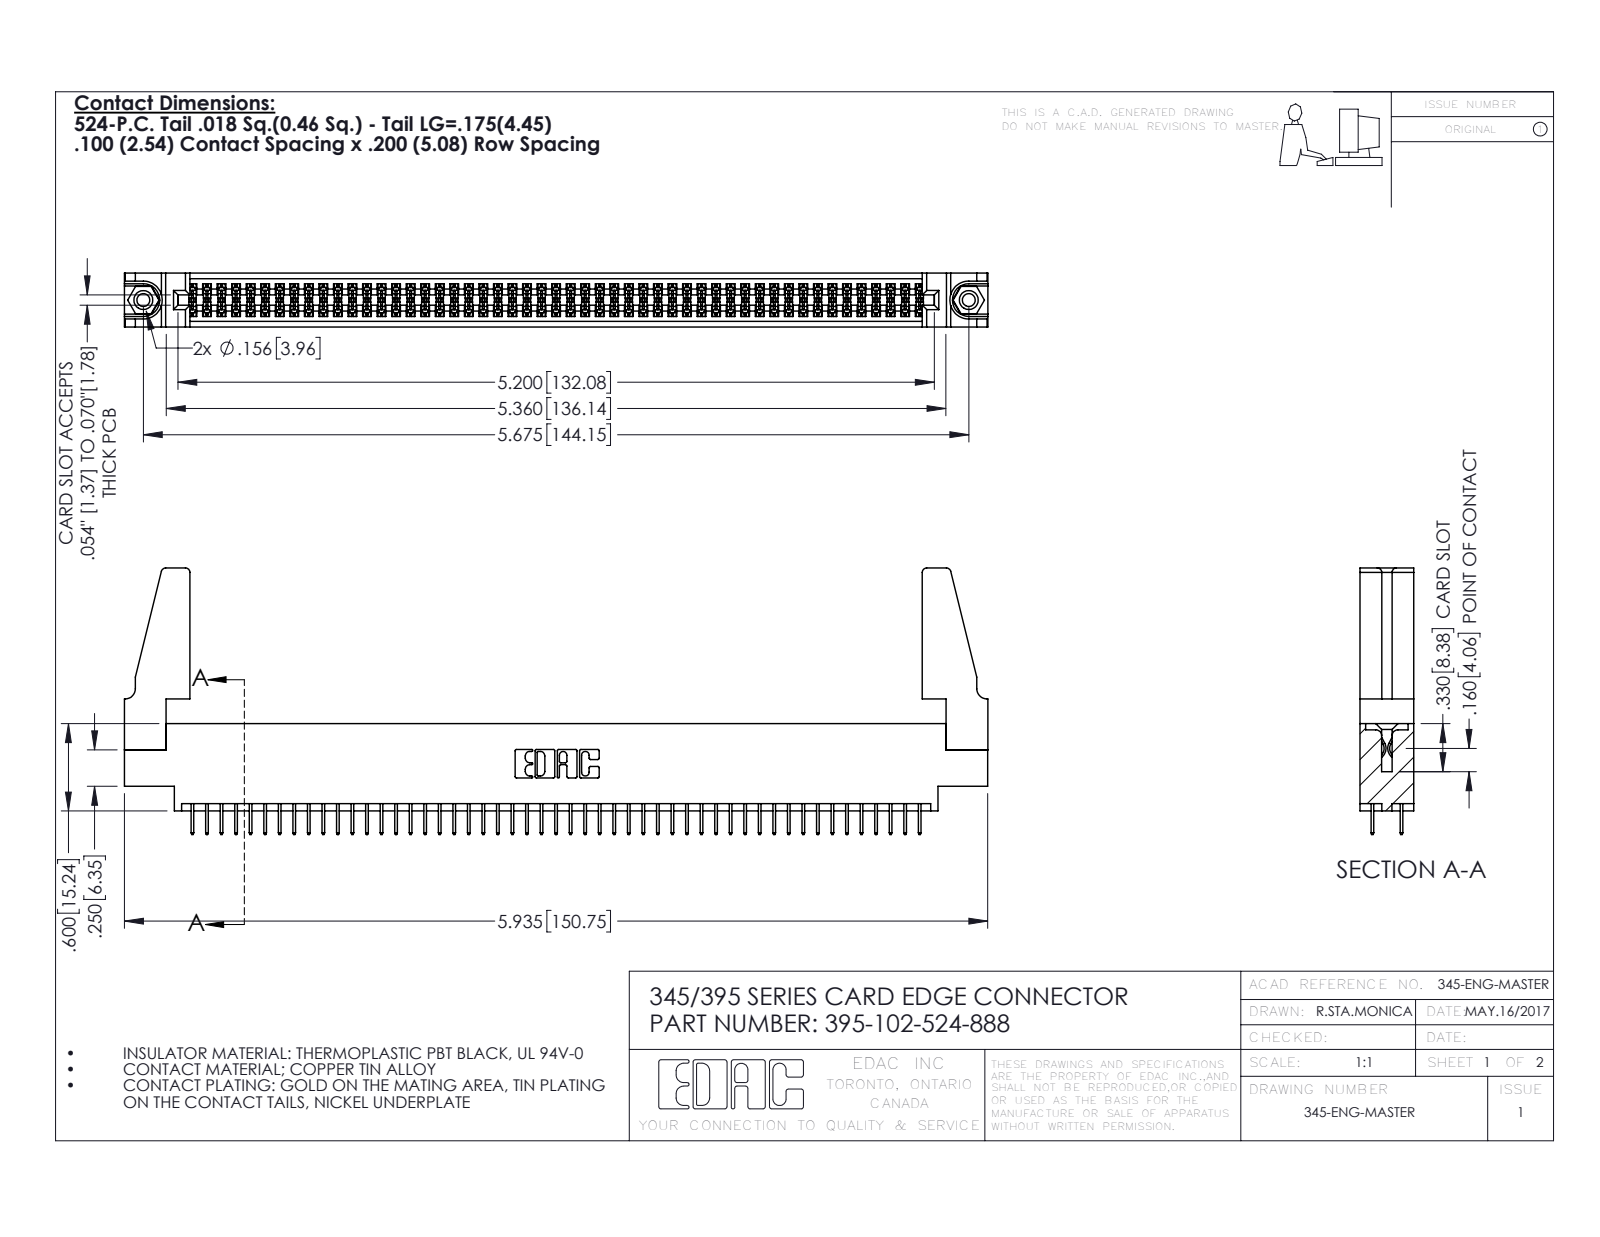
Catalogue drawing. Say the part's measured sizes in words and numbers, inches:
The part is named "395-102-524-888; 345-220-078_345-220-088; 345-250-001_345-250-001-102; 345 Part_0.170 Offset - 0.156 Dia-TH (+1 more)". Its 3-D file was written by "SolidWorks 2016 (CONFIG_CONTROL_DESIGN)". It is 107 solids with 5762 faces: 4134 planar, 1612 cylindrical and 16 other. Overall it measures 5.936 by 1.832 by 0.37 inches. Its volume is 1.081 cubic inches and its surface area 37.84 square inches. Round holes: 2 of diameter 0.089, 2 of diameter 0.125, 2 of diameter 0.156, 1 of diameter 0.064. Round bosses or shafts: 2 of diameter 0.155. Partial cylindrical surfaces (rounded edges, fillets, slot ends): 153 of radius 0.006, 22 of radius 0.01, 8 of radius 0.03, 6 of radius 0.007, 6 of radius 0.031, 3 of radius 0.026, 2 of radius 0.014, 2 of radius 0.019. The main face-to-face distances are 0.072, 0.298, 0.37, 0.2, 0.098, 0.272, 0.025, 0.225, 0.072, 0.175. The hole center spacings are 0.27, 5.439, 5.675.
